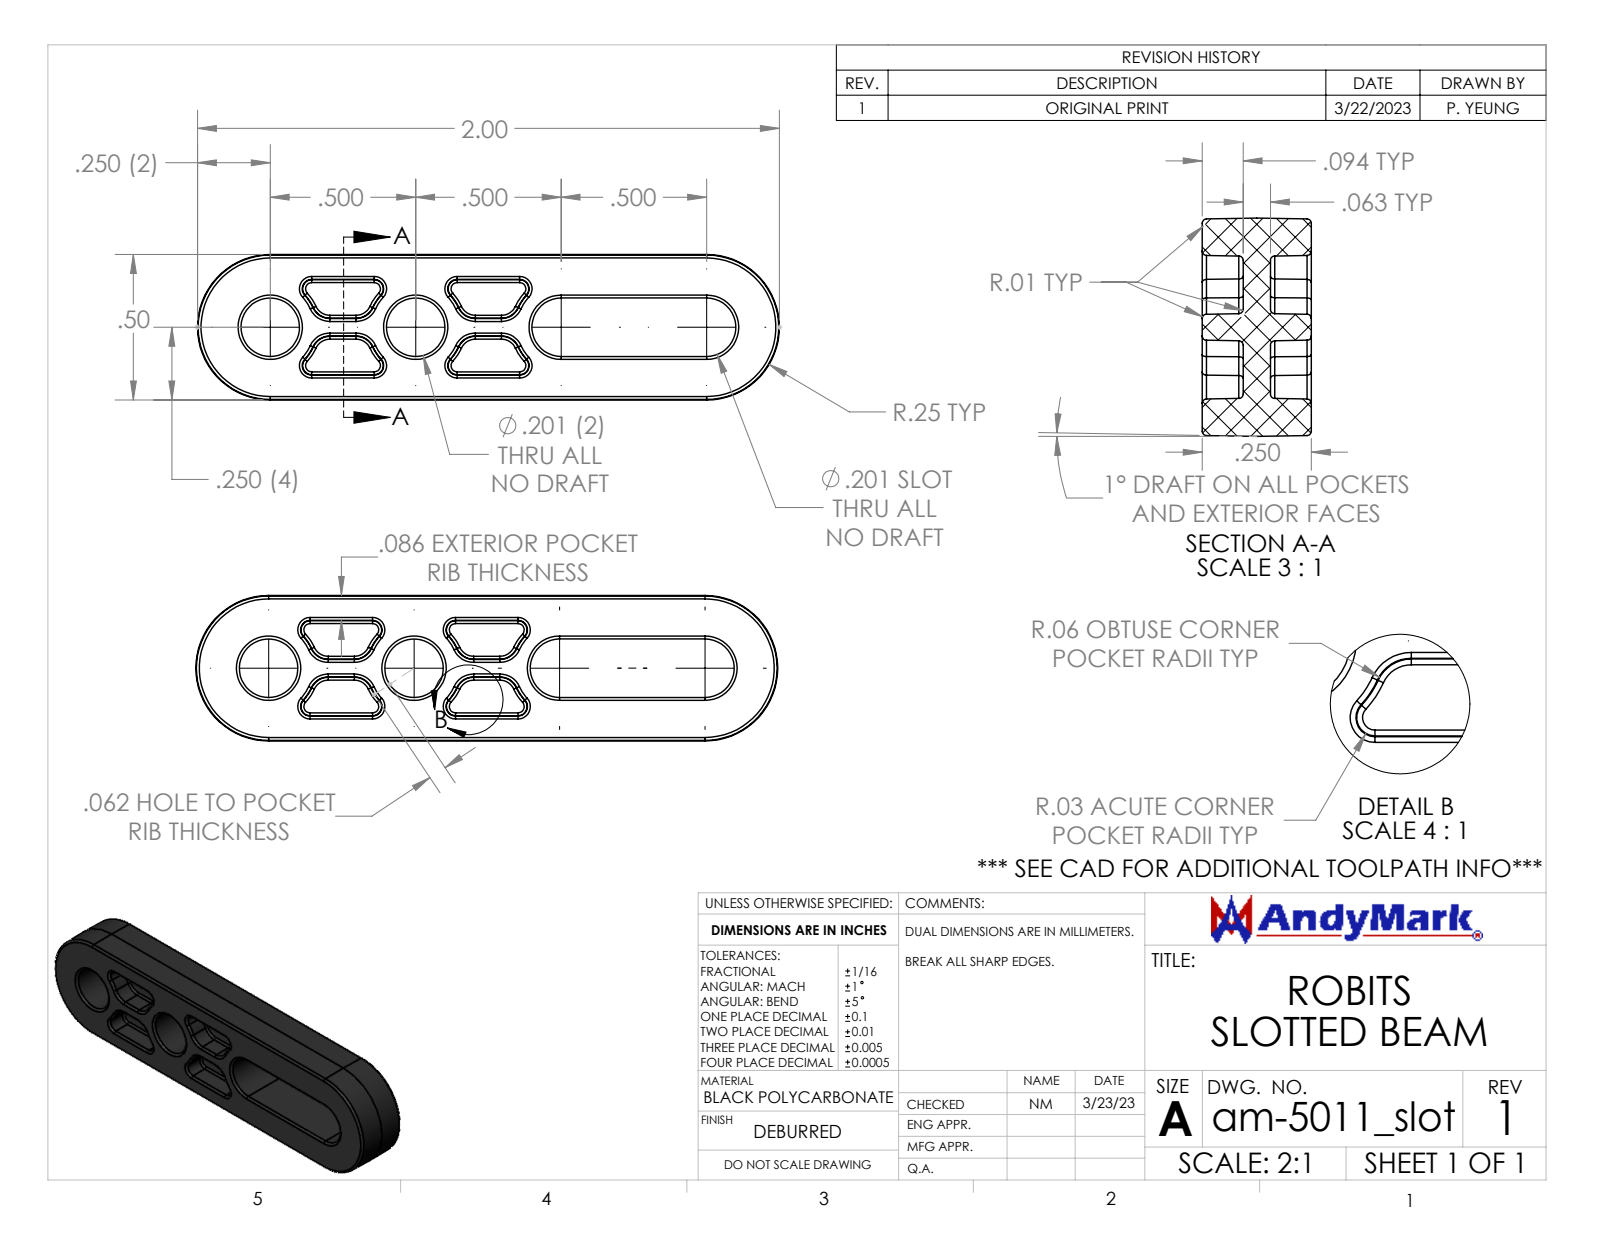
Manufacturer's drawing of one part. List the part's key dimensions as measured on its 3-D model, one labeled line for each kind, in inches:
Part name (STEP PRODUCT): am-5011_slot RoBits Slotted Beam
STEP written by: SolidWorks 2022 (CONFIG_CONTROL_DESIGN)
Units: inches
Bodies: 1 solid, 242 faces (32 planar, 46 cylindrical, 164 other)
Overall size (bounding box): 2 × 0.5 × 0.25
Volume: 0.163 in³ · Surface area: 3.754 in²
Round holes (diameter × count): ⌀0.201 ×2
Partial cylindrical surfaces — rounded edges, fillets, slot ends (radius × count): R0.01 ×24, R0.101 ×2
Main face-to-face distances: 0.25, 0.5, 0.094, 0.156, 0.087, 0.413, 0.201, 0.062, 0.325, 0.218
Hole centre spacings: 0.5
